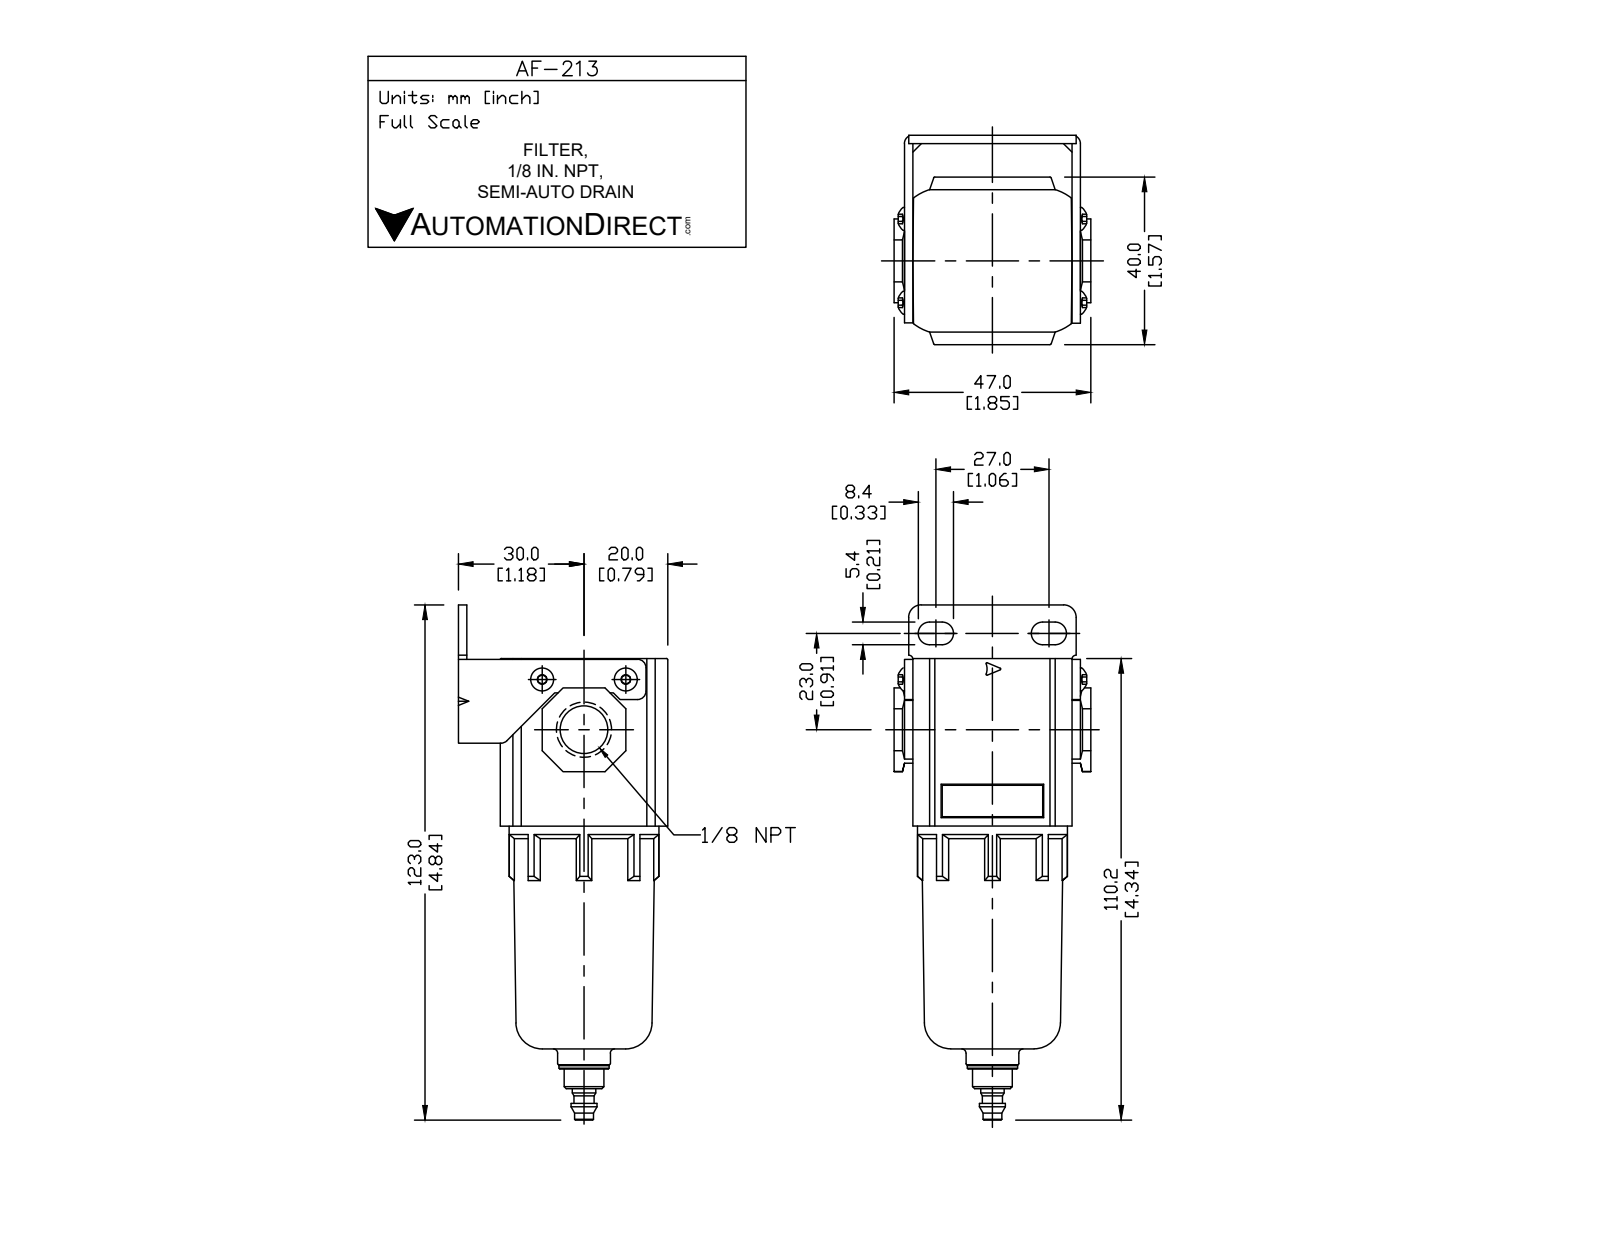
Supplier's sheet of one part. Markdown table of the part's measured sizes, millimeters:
| quantity | value |
| --- | --- |
| part name | AF-213 |
| STEP written by | SolidWorks 2015 (CONFIG_CONTROL_DESIGN) |
| units | millimeters |
| bodies | 8 solids, 313 faces (183 planar, 84 cylindrical, 46 other) |
| overall size | 123 × 50 × 47 |
| volume | 94 049 mm³ |
| surface area | 29 180 mm² |
| round holes (diameter × count) | 3.4 × 2, 3 × 1, 8.43 × 1, 24.8 × 1, 25 × 1 |
| round bosses / shafts (diameter × count) | 36 × 1, 34 × 1, 19 × 1, 12.6 × 1, 12 × 1, 9.5 × 1, 7 × 1, 6.2 × 1 |
| partial cylindrical surfaces (radius × count) | 2 × 5, 0.3 × 4, 2.7 × 4, 12 × 4, 3 × 2, 4 × 2, 16.9 × 1, 17.9 × 1 |
| main face-to-face distances | 40, 2, 38, 50, 10, 8, 48, 4.5, 42, 2.5 |
| hole center spacings | 15.62, 20 |
